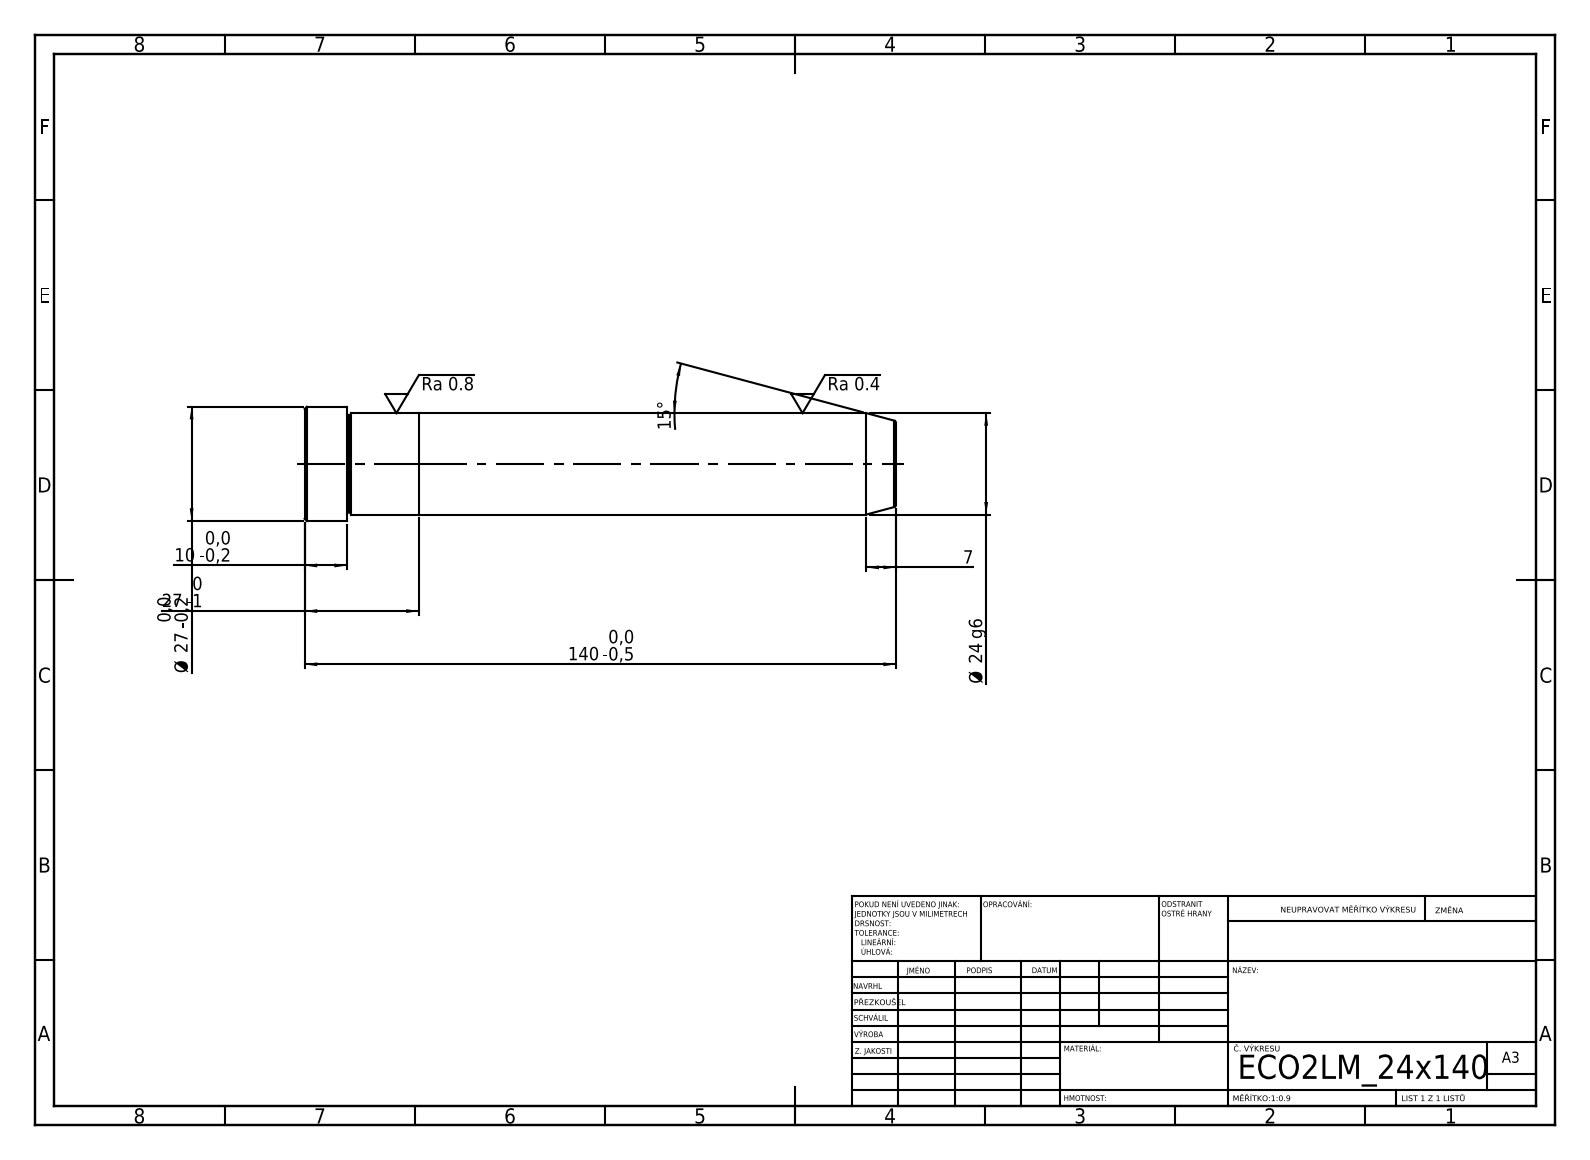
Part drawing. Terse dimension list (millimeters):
written by: SolidWorks 2019 (CONFIG_CONTROL_DESIGN)
unit: mm
bodies: 2 solids, 21 faces (5 planar, 6 cylindrical, 10 other)
size: 140 × 27 × 27
volume: 64 026 mm³; area: 12 553 mm²
bosses: 1× ⌀27, 1× ⌀24
face distances: 27, 113, 140, 130, 17, 10
